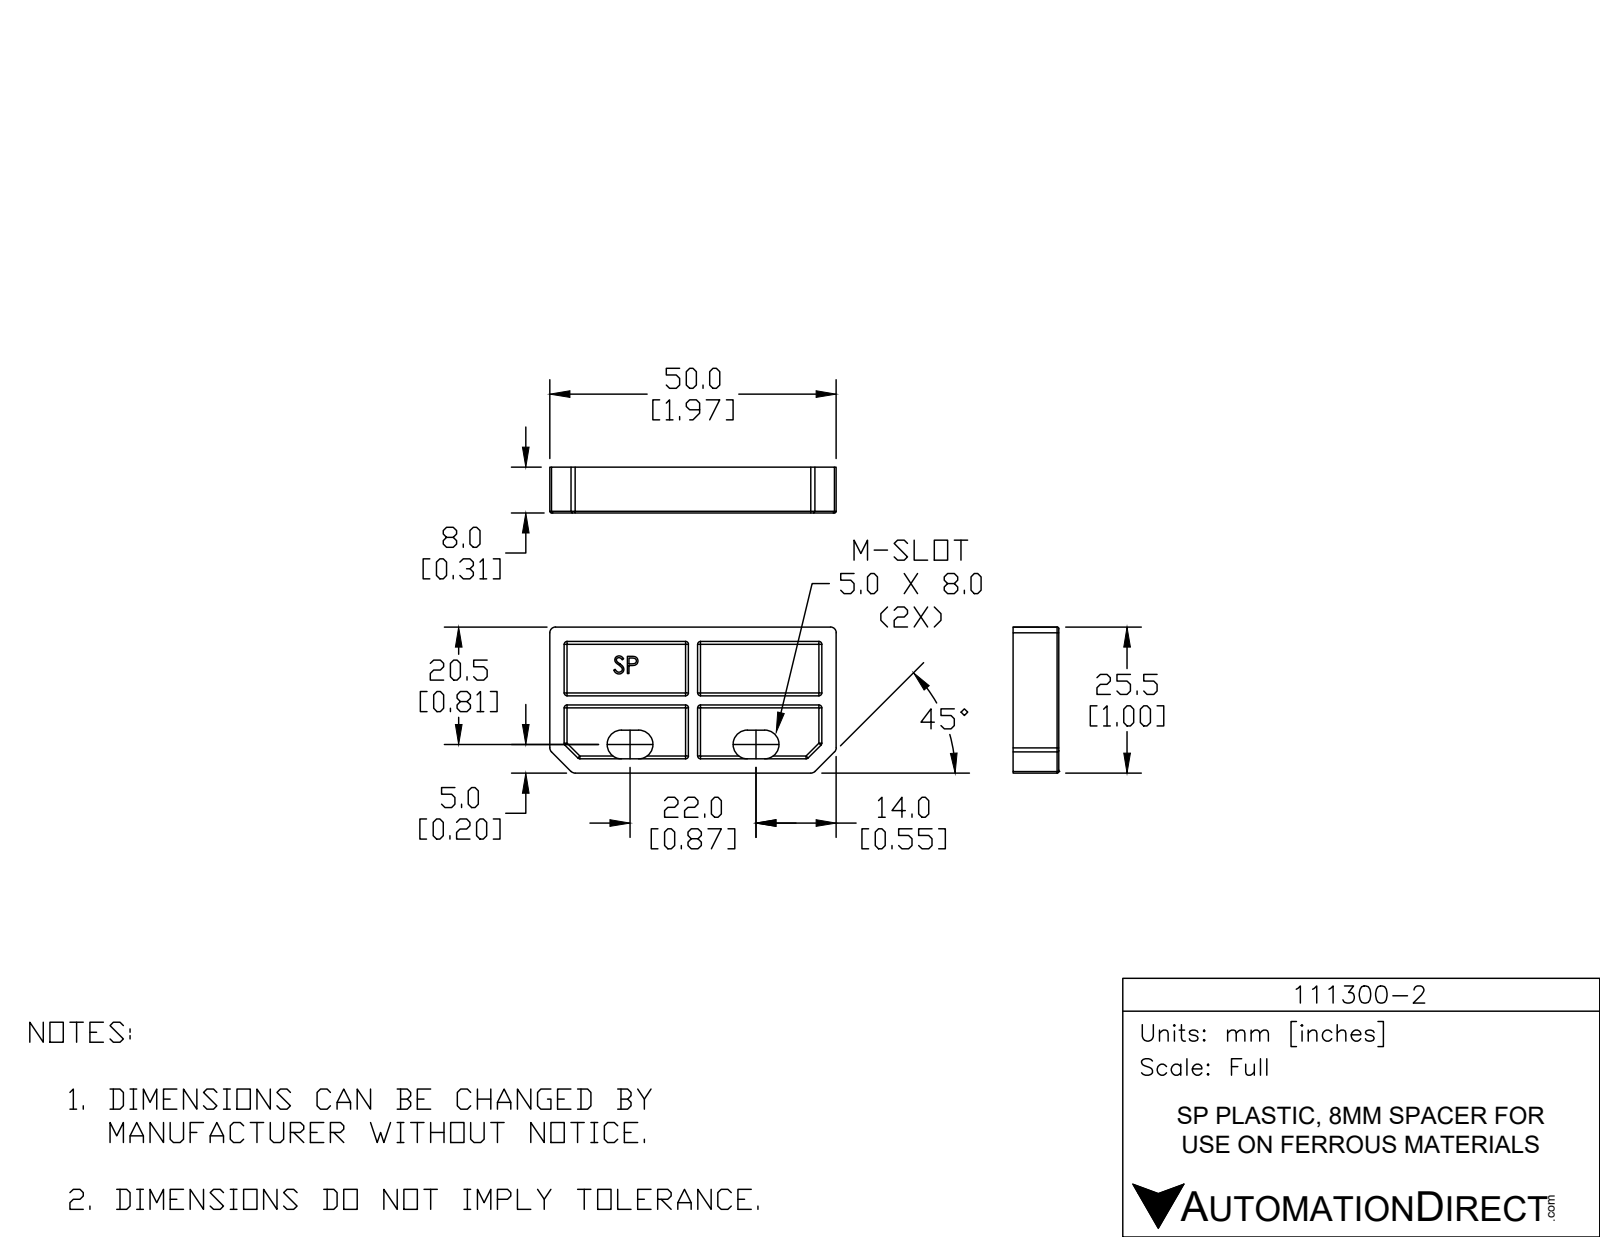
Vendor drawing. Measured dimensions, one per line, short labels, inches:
name: 111-SP Spacer
written by: SolidWorks 2018 (CONFIG_CONTROL_DESIGN)
unit: in
bodies: 1 solid, 156 faces (49 planar, 56 cylindrical, 51 other)
size: 1.969 × 1.004 × 0.315
volume: 0.353 in³; area: 7.443 in²
rounds: 28× R0.02, 6× R0.012, 6× R0.039, 4× R0.098
face distances: 0.118, 0.098, 0.197, 0.315, 0.906, 1.004, 0.063, 0.535, 0.437, 0.469
